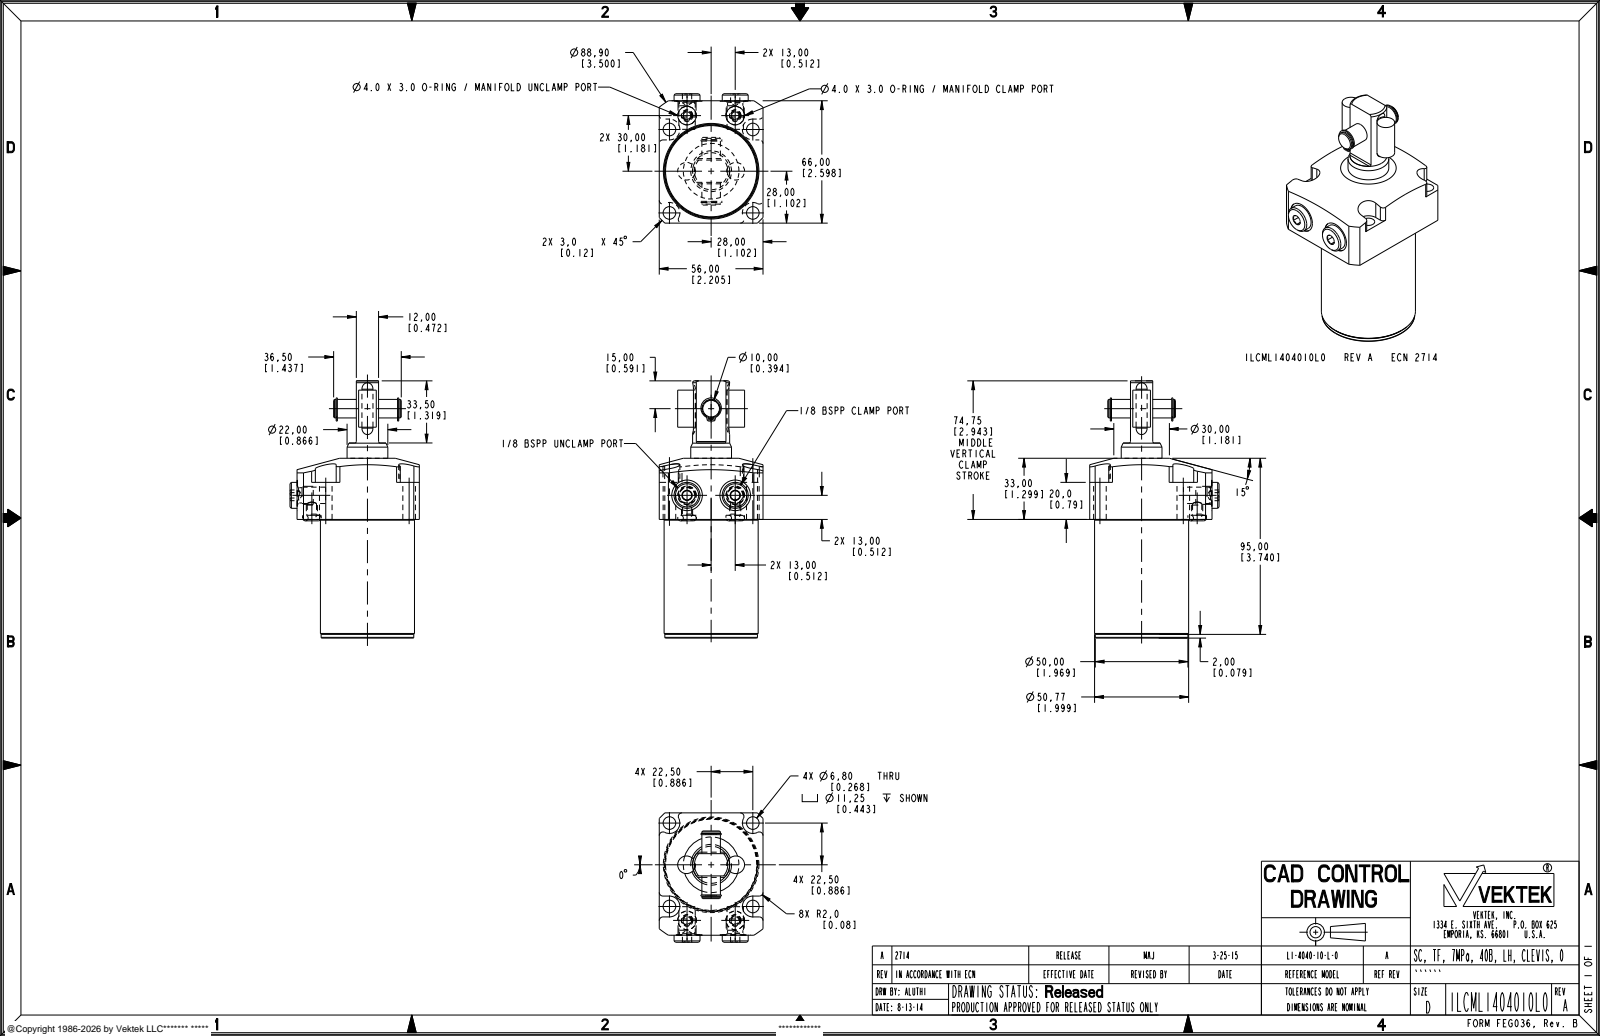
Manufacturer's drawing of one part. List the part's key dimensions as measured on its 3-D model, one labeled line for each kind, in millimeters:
Part name (STEP PRODUCT): ILCML1404010L0
STEP written by: PRO/ENGINEER BY PARAMETRIC TECHNOLOGY CORPORATION, 2013320 (AUTOMOTIVE_DESIGN)
Units: millimetres
Bodies: 5 solids, 245 faces (85 planar, 104 cylindrical, 56 other)
Overall size (bounding box): 138.75 × 69.81 × 56
Volume: 248 568 mm³ · Surface area: 33 941 mm²
Round holes (diameter × count): ⌀5 ×4, ⌀6.8 ×4, ⌀1.04 ×2, ⌀8.84 ×2, ⌀10 ×2, ⌀16.5 ×2
Round bosses / shafts (diameter × count): ⌀14 ×2, ⌀9.73 ×2, ⌀9.53 ×2, ⌀8.25 ×2, ⌀6 ×2, ⌀50.77 ×1, ⌀50 ×1, ⌀22 ×1
Partial cylindrical surfaces — rounded edges, fillets, slot ends (radius × count): R2 ×8, R5.62 ×4, R0.8 ×2, R1.04 ×2, R1.48 ×2, R4.76 ×2, R44.45 ×1
Main face-to-face distances: 56, 64, 66, 22, 44, 34, 12, 32, 20, 13
Hole centre spacings: 45, 12.1, 26, 36.28, 42.76, 43.46, 53.35, 63.38
